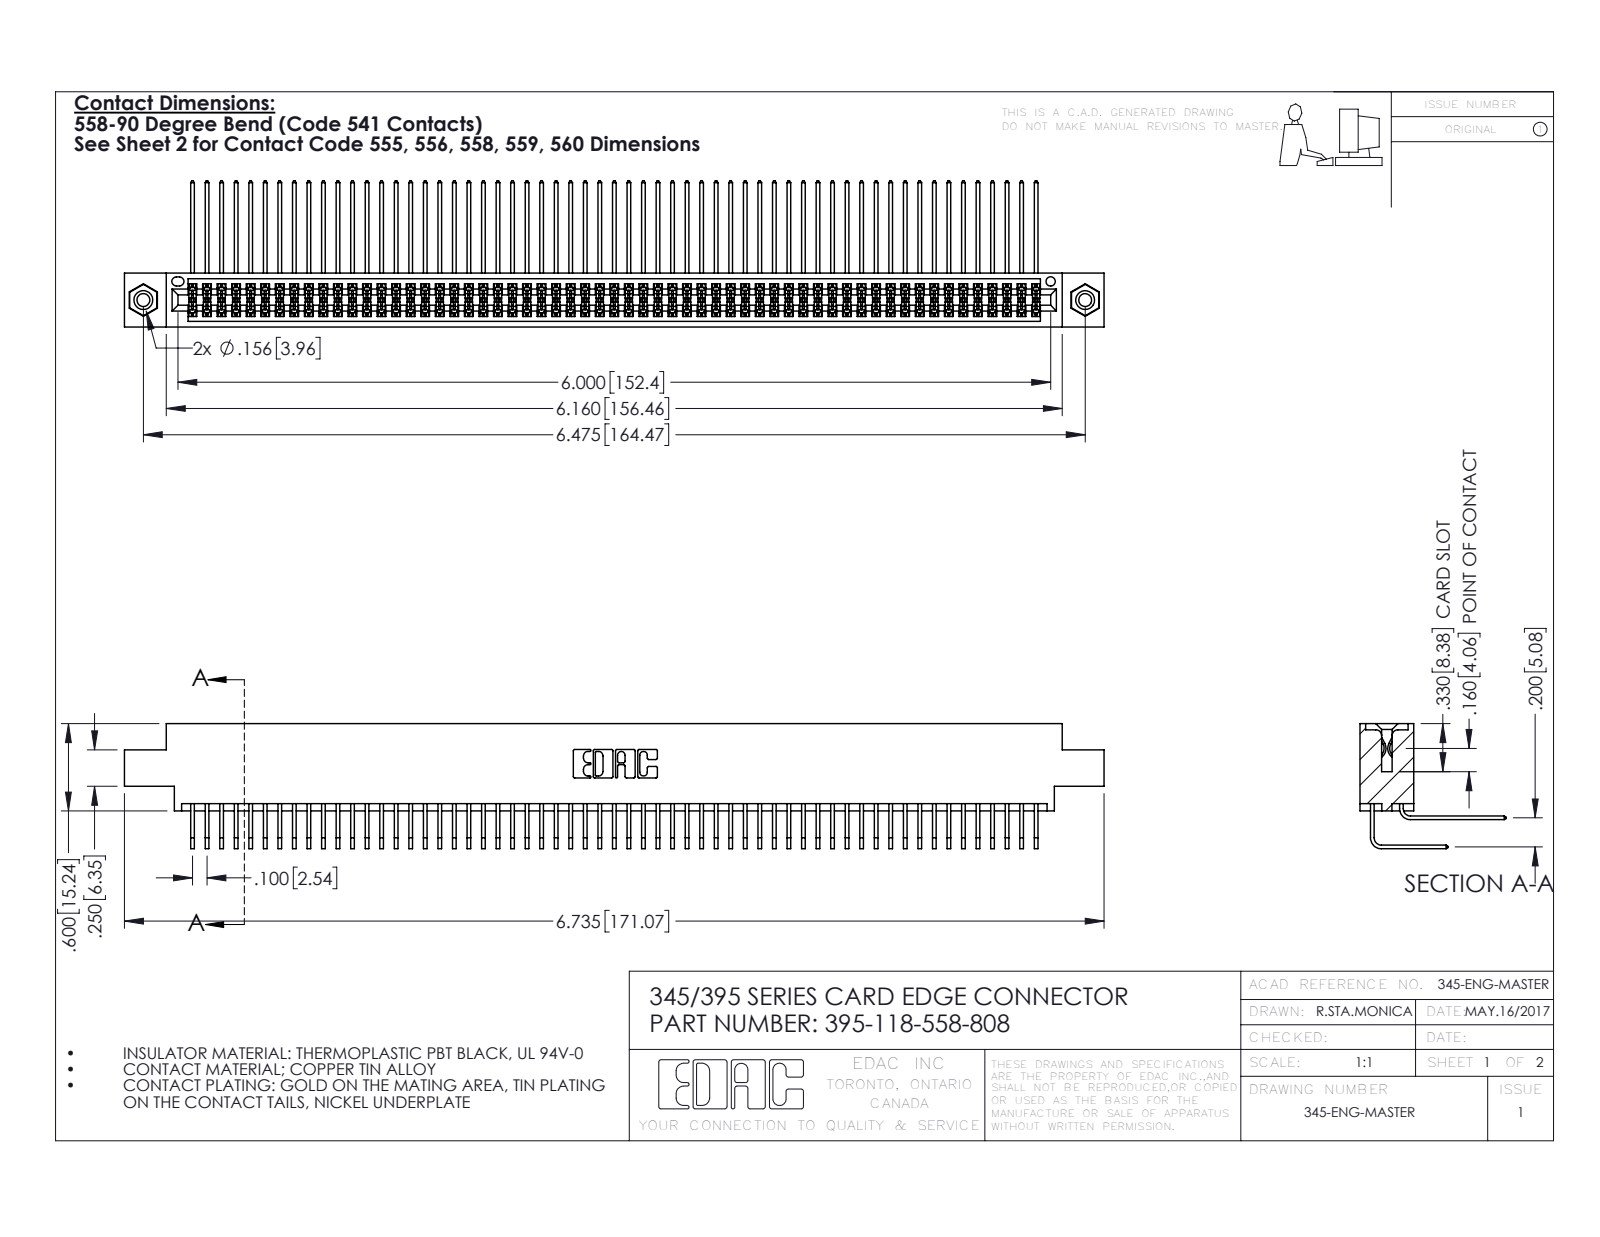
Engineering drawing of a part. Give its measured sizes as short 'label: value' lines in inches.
name: 345-250-001_345-250-003-102; 345-292-001_558 Tail - 2; 395-118-558-808; 345-292-001_558 559 Tail - 1 (+1 more)
written by: SolidWorks 2016 (CONFIG_CONTROL_DESIGN)
unit: in
bodies: 121 solids, 6326 faces (4246 planar, 2064 cylindrical, 16 other)
size: 6.735 × 1.005 × 0.859
volume: 1.058 in³; area: 45.44 in²
holes: 2× ⌀0.089, 2× ⌀0.125, 2× ⌀0.156, 1× ⌀0.064
bosses: 2× ⌀0.155
rounds: 178× R0.006, 22× R0.01, 6× R0.007, 6× R0.031, 3× R0.026, 2× R0.014, 2× R0.019, 2× R0.022
face distances: 0.072, 0.298, 0.2, 0.37, 0.098, 0.272, 0.025, 0.225, 0.175, 0.025
hole spacings: 0.27, 6.239, 6.475
